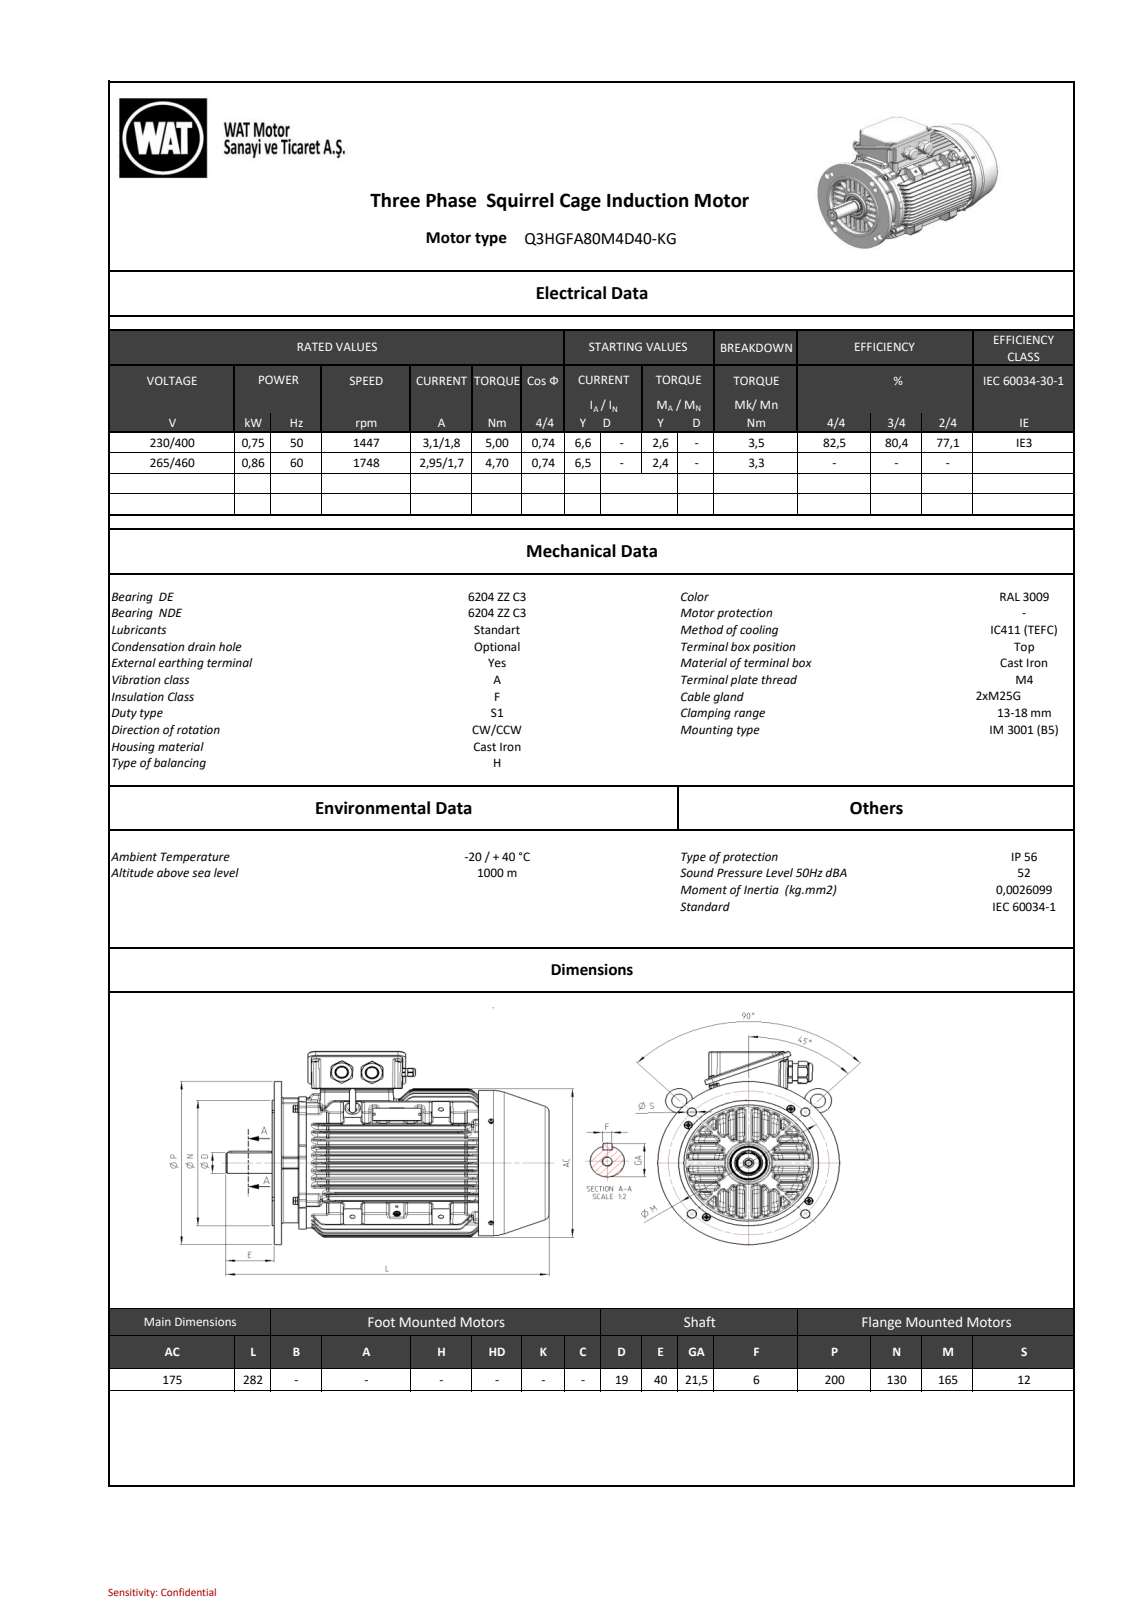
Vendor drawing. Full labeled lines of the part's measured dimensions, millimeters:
Part name (STEP PRODUCT): C90125944CFF0j0m
STEP written by: SIEMENS PLM Software NX 11.0 (AUTOMOTIVE_DESIGN)
Units: millimetres
Bodies: 0 solids, 2952 faces (792 planar, 840 cylindrical, 1320 other)
Overall size (bounding box): 281.76 × 244.98 × 221.33
Round holes (diameter × count): ⌀10 ×6, ⌀12 ×4, ⌀2.5 ×2, ⌀17.2 ×2, ⌀5 ×1, ⌀6.4 ×1, ⌀6.5 ×1, ⌀27.8 ×1, ⌀28 ×1, ⌀168 ×1
Round bosses / shafts (diameter × count): ⌀20 ×4, ⌀8.65 ×3, ⌀8 ×3, ⌀5 ×3, ⌀27.7 ×2, ⌀25.25 ×2, ⌀200 ×1, ⌀170 ×1
Partial cylindrical surfaces — rounded edges, fillets, slot ends (radius × count): R1.5 ×348, R2.5 ×57, R2 ×53, R1 ×24, R4 ×20, R7 ×13, R5 ×12, R26.5 ×12
Main face-to-face distances: 5, 194.98, 199.98, 41.78, 236.76, 241.76, 62.56, 3.01, 1.5, 229.61
Hole centre spacings: 116.67, 133.37, 21.53, 61.25, 77, 82.5, 97.19, 126.58
